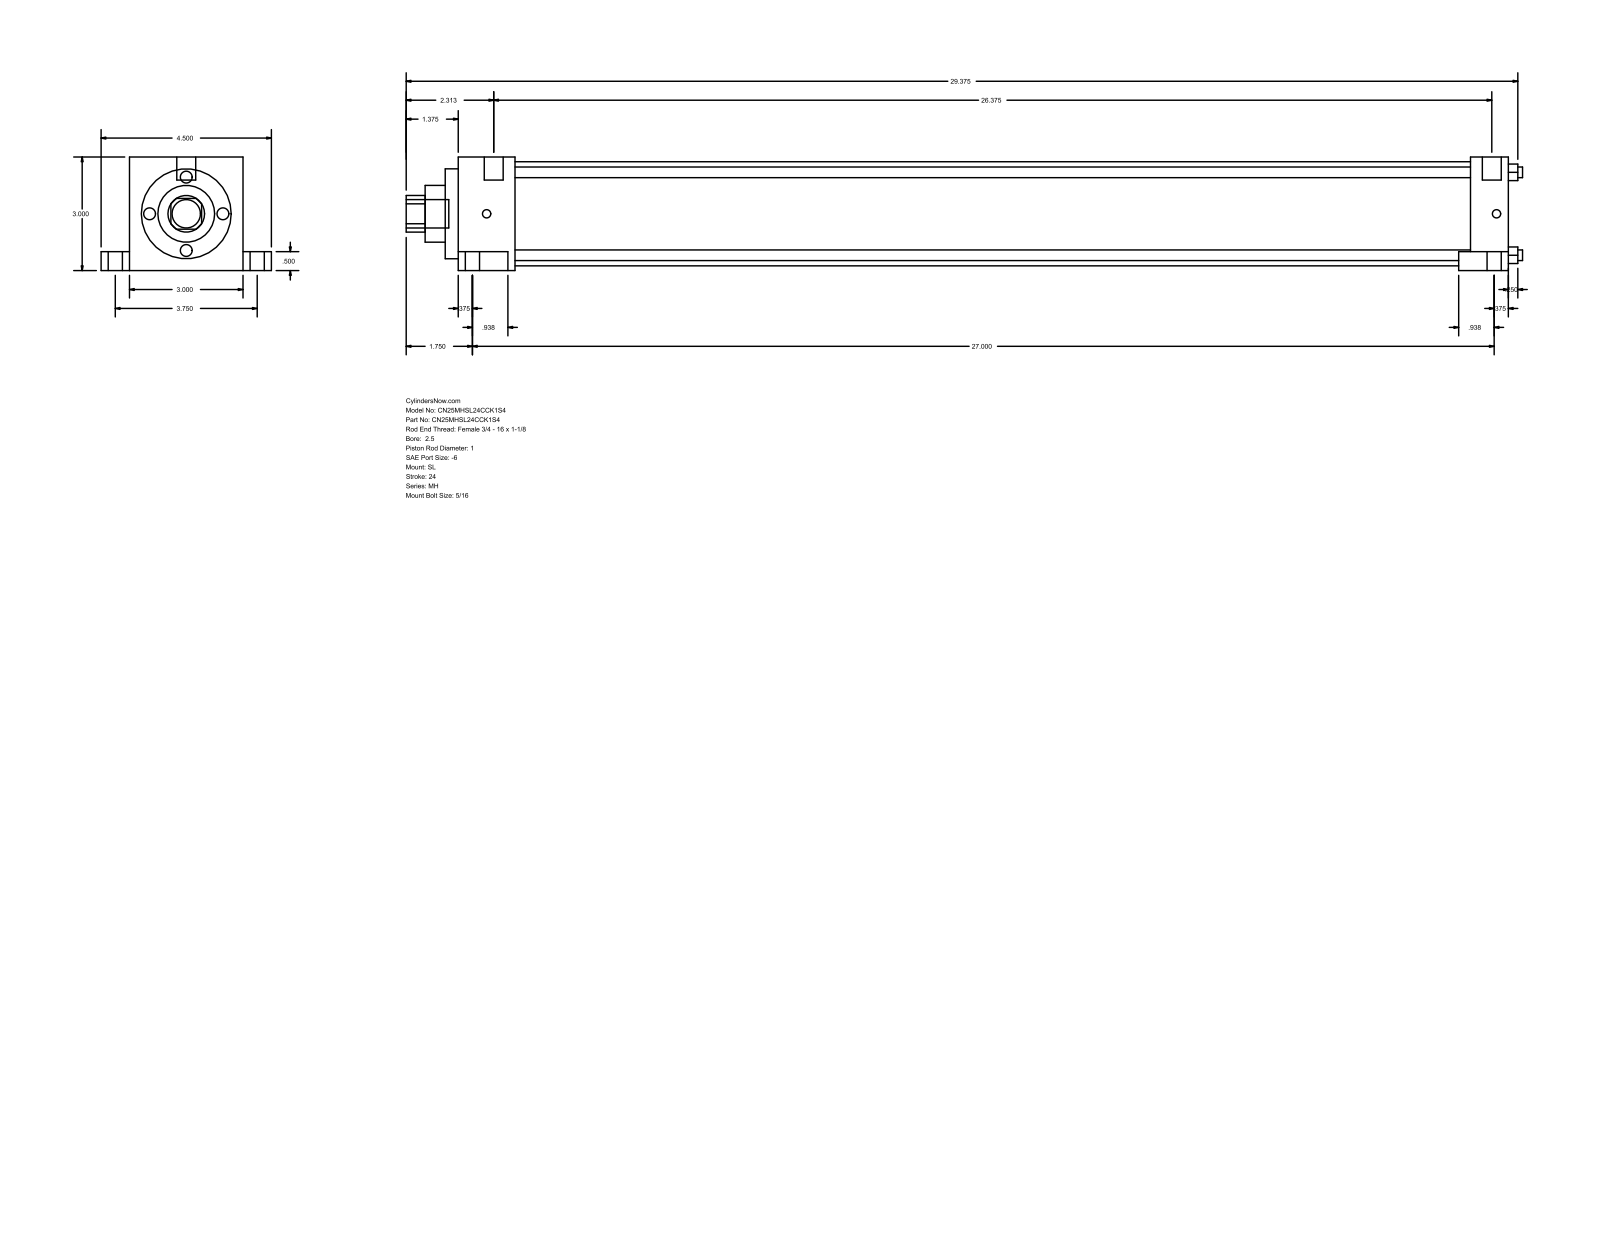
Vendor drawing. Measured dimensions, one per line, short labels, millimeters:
name: MH_SL__0250_1
written by: GSSL Pune (CONFIG_CONTROL_DESIGN)
unit: mm
bodies: 0 solids, 86 faces (61 planar, 25 cylindrical, 0 other)
size: 749.3 × 114.3 × 76.2
holes: 4× ⌀7.14, 1× ⌀25.4, 1× ⌀38.1, 1× ⌀60.33, 1× ⌀69.85
bosses: 2× ⌀15.88, 2× ⌀9.53, 2× ⌀5.56, 1× ⌀19.05, 1× ⌀12.7
rounds: 1× R12.29
face distances: 76.2, 25.39, 688.19, 713.58, 12.7, 63.5, 19.05, 95.25, 13.49, 701.68
hole spacings: 39.33, 55.62, 78.66
